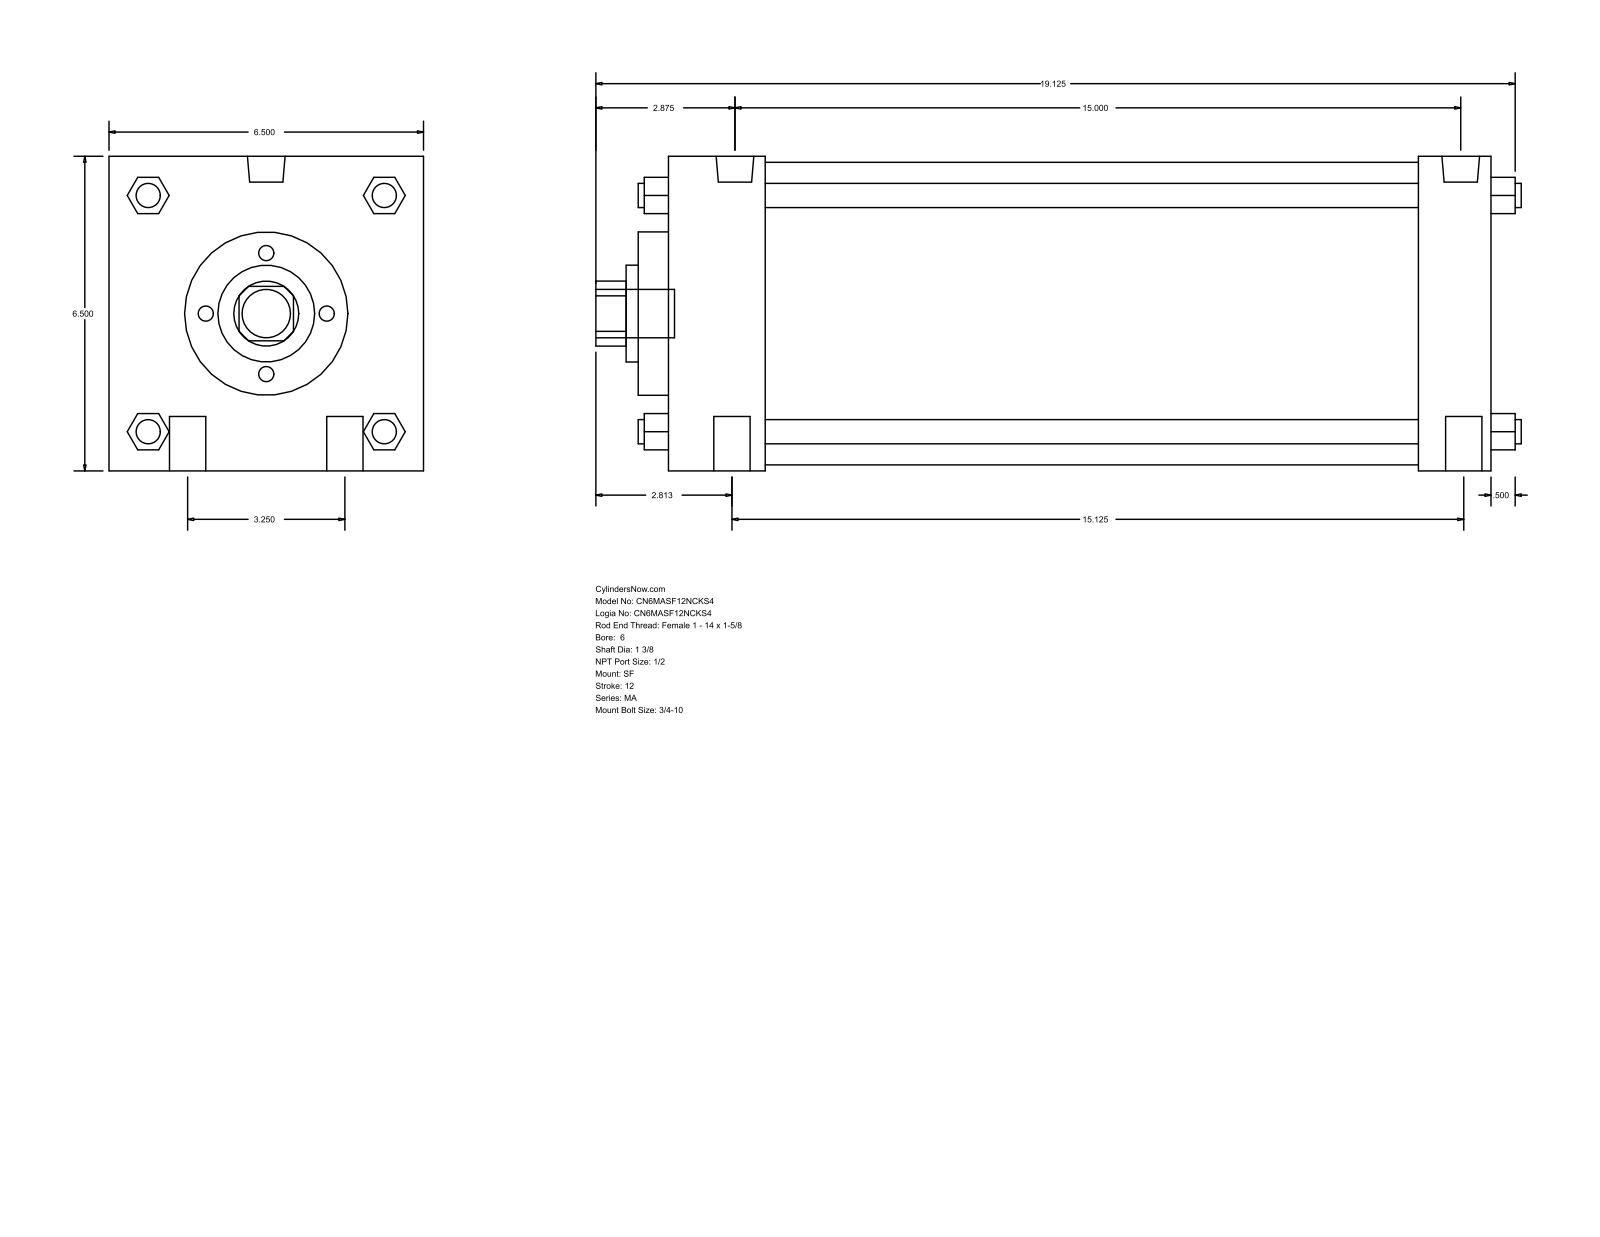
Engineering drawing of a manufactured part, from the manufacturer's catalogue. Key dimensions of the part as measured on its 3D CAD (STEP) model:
Part name (STEP PRODUCT): MA_SF__0600_1.375
STEP written by: GSSL Pune (CONFIG_CONTROL_DESIGN)
Units: millimetres
Bodies: 0 solids, 126 faces (95 planar, 31 cylindrical, 0 other)
Overall size (bounding box): 485.77 × 165.1 × 165.1
Round holes (diameter × count): ⌀34.92 ×1, ⌀50.8 ×1, ⌀85.72 ×1, ⌀158.75 ×1
Round bosses / shafts (diameter × count): ⌀19.05 ×4, ⌀12.7 ×4, ⌀19.77 ×2, ⌀17.46 ×2, ⌀25.4 ×1
Partial cylindrical surfaces — rounded edges, fillets, slot ends (radius × count): R17.06 ×1
Main face-to-face distances: 165.1, 431.8, 393.7, 50.8, 38.1, 342.9, 381, 15.87, 447.67, 66.67
